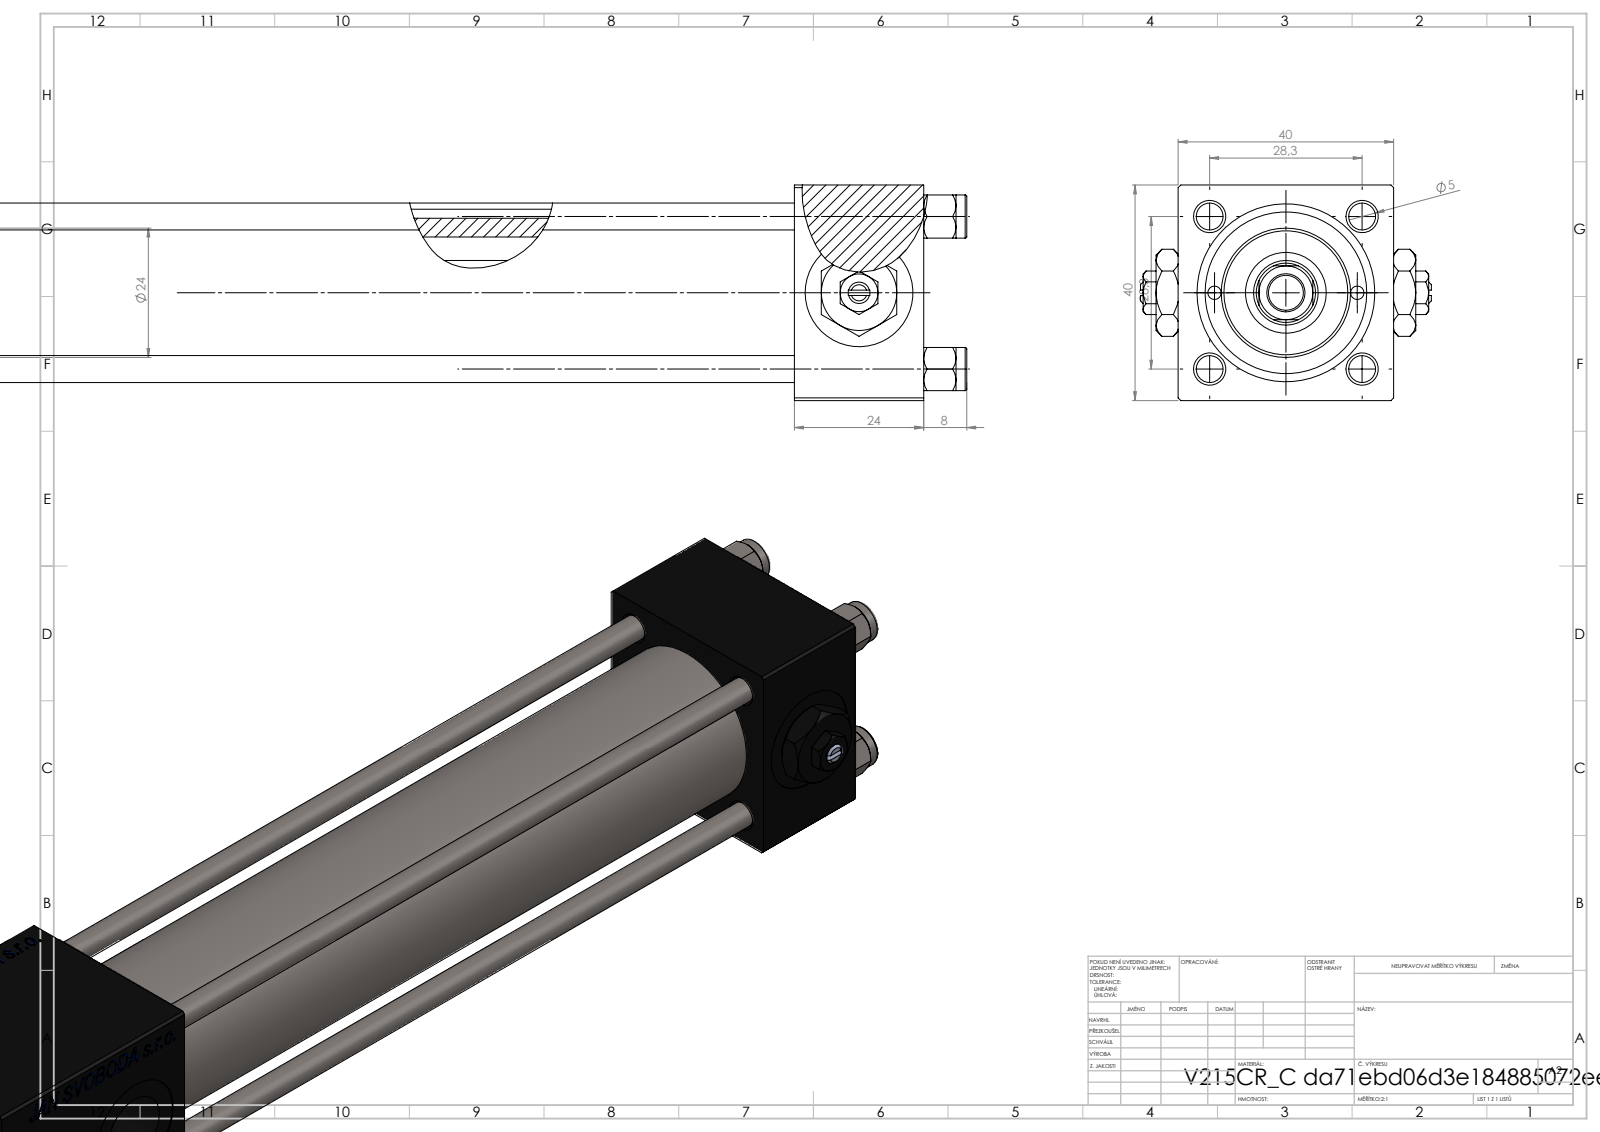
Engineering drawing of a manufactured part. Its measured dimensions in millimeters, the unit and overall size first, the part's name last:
Units: millimetres
Overall size (bounding box): 247 × 54 × 40
Round holes (diameter × count): ⌀5 ×4, ⌀20 ×3, ⌀2.5 ×2, ⌀7 ×2, ⌀13.16 ×2, ⌀6.5 ×1, ⌀12 ×1, ⌀15 ×1, ⌀25 ×1, ⌀30 ×1
Round bosses / shafts (diameter × count): ⌀8 ×4, ⌀31 ×1, ⌀24 ×1
Partial cylindrical surfaces — rounded edges, fillets, slot ends (radius × count): R5.5 ×1
Main face-to-face distances: 40, 24, 39.8, 195.3, 171.3, 48, 176, 152, 19.3, 200
Hole centre spacings: 14.18, 20.01, 28.3, 30.84, 13.25, 40.02, 26.5, 177
Volume: 188 767 mm³ · Surface area: 85 316 mm²
Bodies: 13 solids, 1254 faces (574 planar, 102 cylindrical, 578 other)
Part name (STEP PRODUCT): V215CR_C_Body; V215CR_VCP_C; NUT_M5_C; Zatka_pro_OIL_PORT (+2 more)
STEP written by: SolidWorks 2019 (CONFIG_CONTROL_DESIGN)
